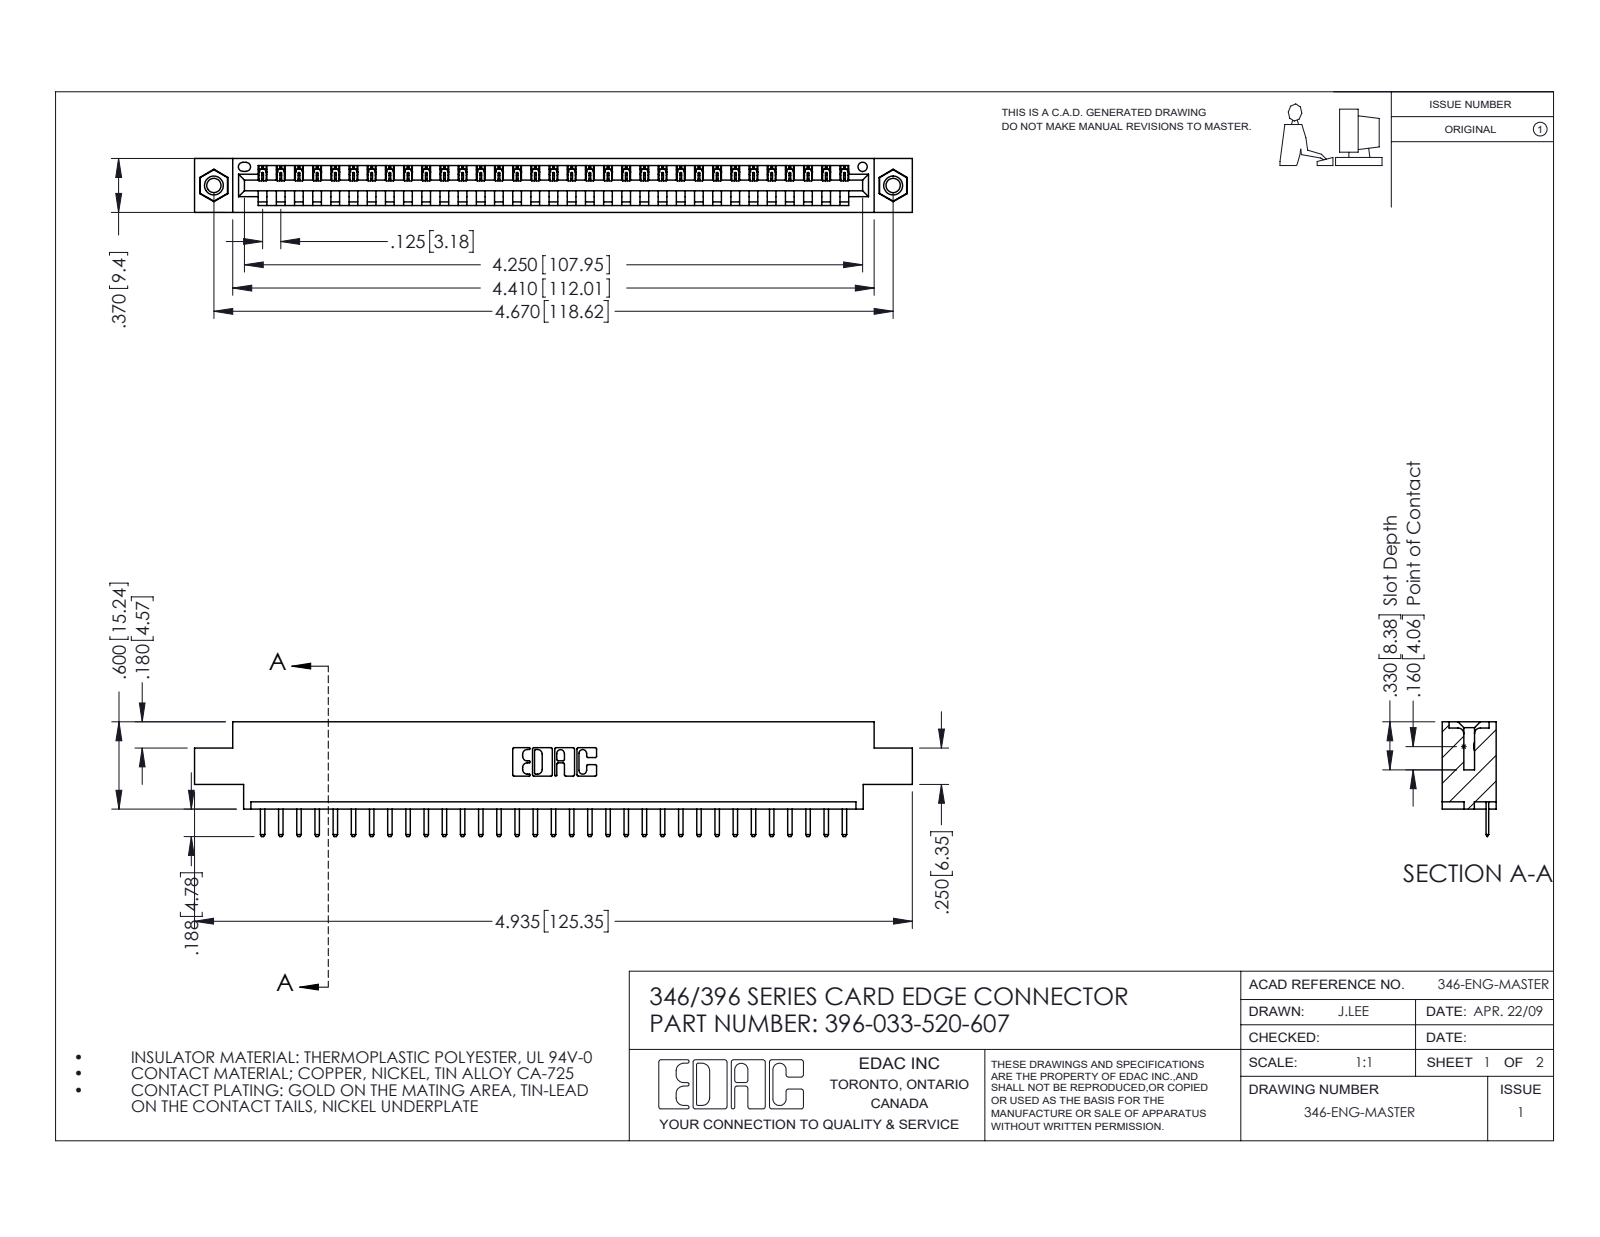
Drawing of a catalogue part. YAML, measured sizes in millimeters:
part_name: "345-250-001_345-250-005-103; 345-292-001_345-293-120; 346 Part_0.170 Offset - 0.156 Dia-TI; 396-033-520-607"
step_written_by: "SolidWorks 2016 (CONFIG_CONTROL_DESIGN)"
units: millimeters
bodies: {solids: 36, faces: 2232, planar: 1498, cylindrical: 718, other: 16}
overall_size: [125.3, 20, 9.4]
volume: 11700
surface_area: 14370
round_holes:
  - {diameter: 2.5, count: 2}
  - {diameter: 3.2, count: 2}
  - {diameter: 4, count: 2}
  - {diameter: 1.6, count: 1}
round_bosses_or_shafts:
  - {diameter: 3.9, count: 2}
partial_cylinders:
  - {radius: 0.3, count: 68}
  - {radius: 0.2, count: 66}
  - {radius: 0.3, count: 22}
  - {radius: 0.2, count: 6}
  - {radius: 0.8, count: 6}
  - {radius: 0.7, count: 3}
  - {radius: 0.8, count: 2}
  - {radius: 1, count: 2}
face_to_face_distances: [1.2, 8.2, 9.4, 6.4, 5.6, 3.8, 2.5, 4.4, 1.8, 7.6]
hole_center_spacings: [6.2, 113.3, 118.6]
